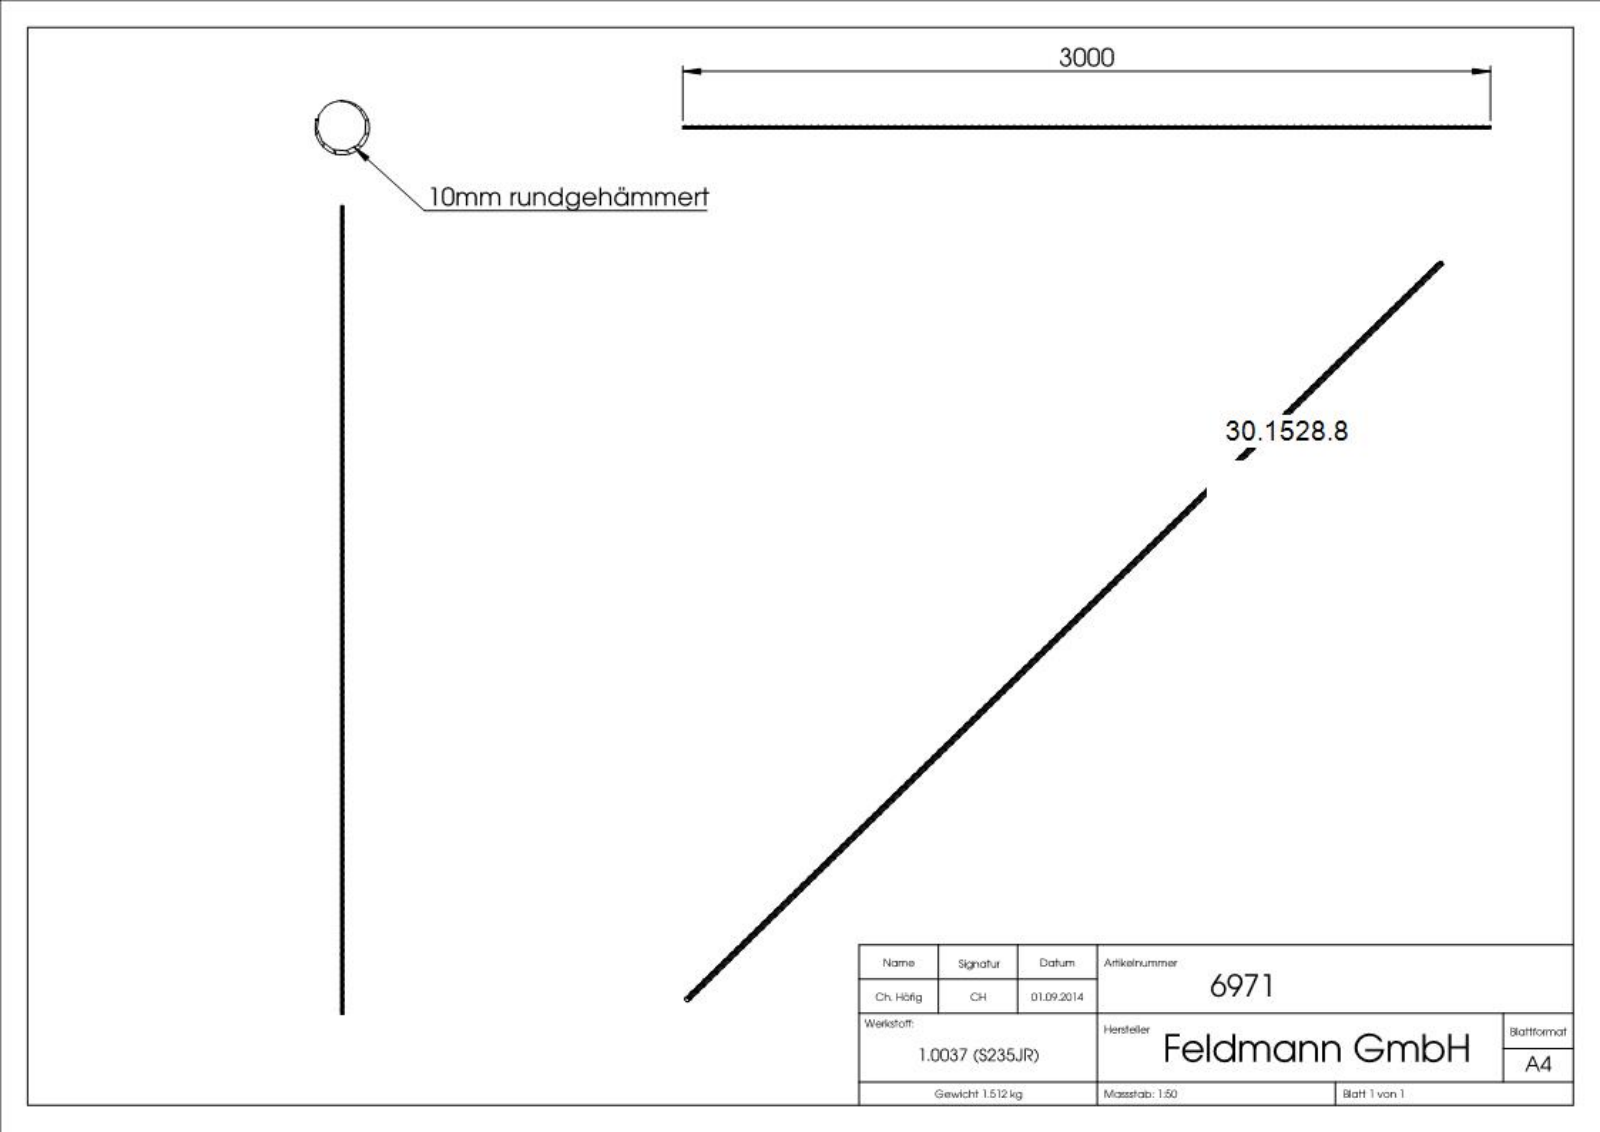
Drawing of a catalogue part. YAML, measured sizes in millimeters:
part_name: "6971"
step_written_by: "SolidWorks 2015 (CONFIG_CONTROL_DESIGN)"
units: millimeters
bodies: {solids: 1, faces: 3476, planar: 67, cylindrical: 3361, other: 48}
overall_size: [3000, 10, 10]
volume: 193508
surface_area: 86600
round_bosses_or_shafts:
  - {diameter: 10, count: 1}
partial_cylinders:
  - {radius: 78.62, count: 1630}
face_to_face_distances: [3000, 1.78, 0.5, 2999.5, 0.44, 0.67, 0.83, 0.99, 1.21, 2.45]
